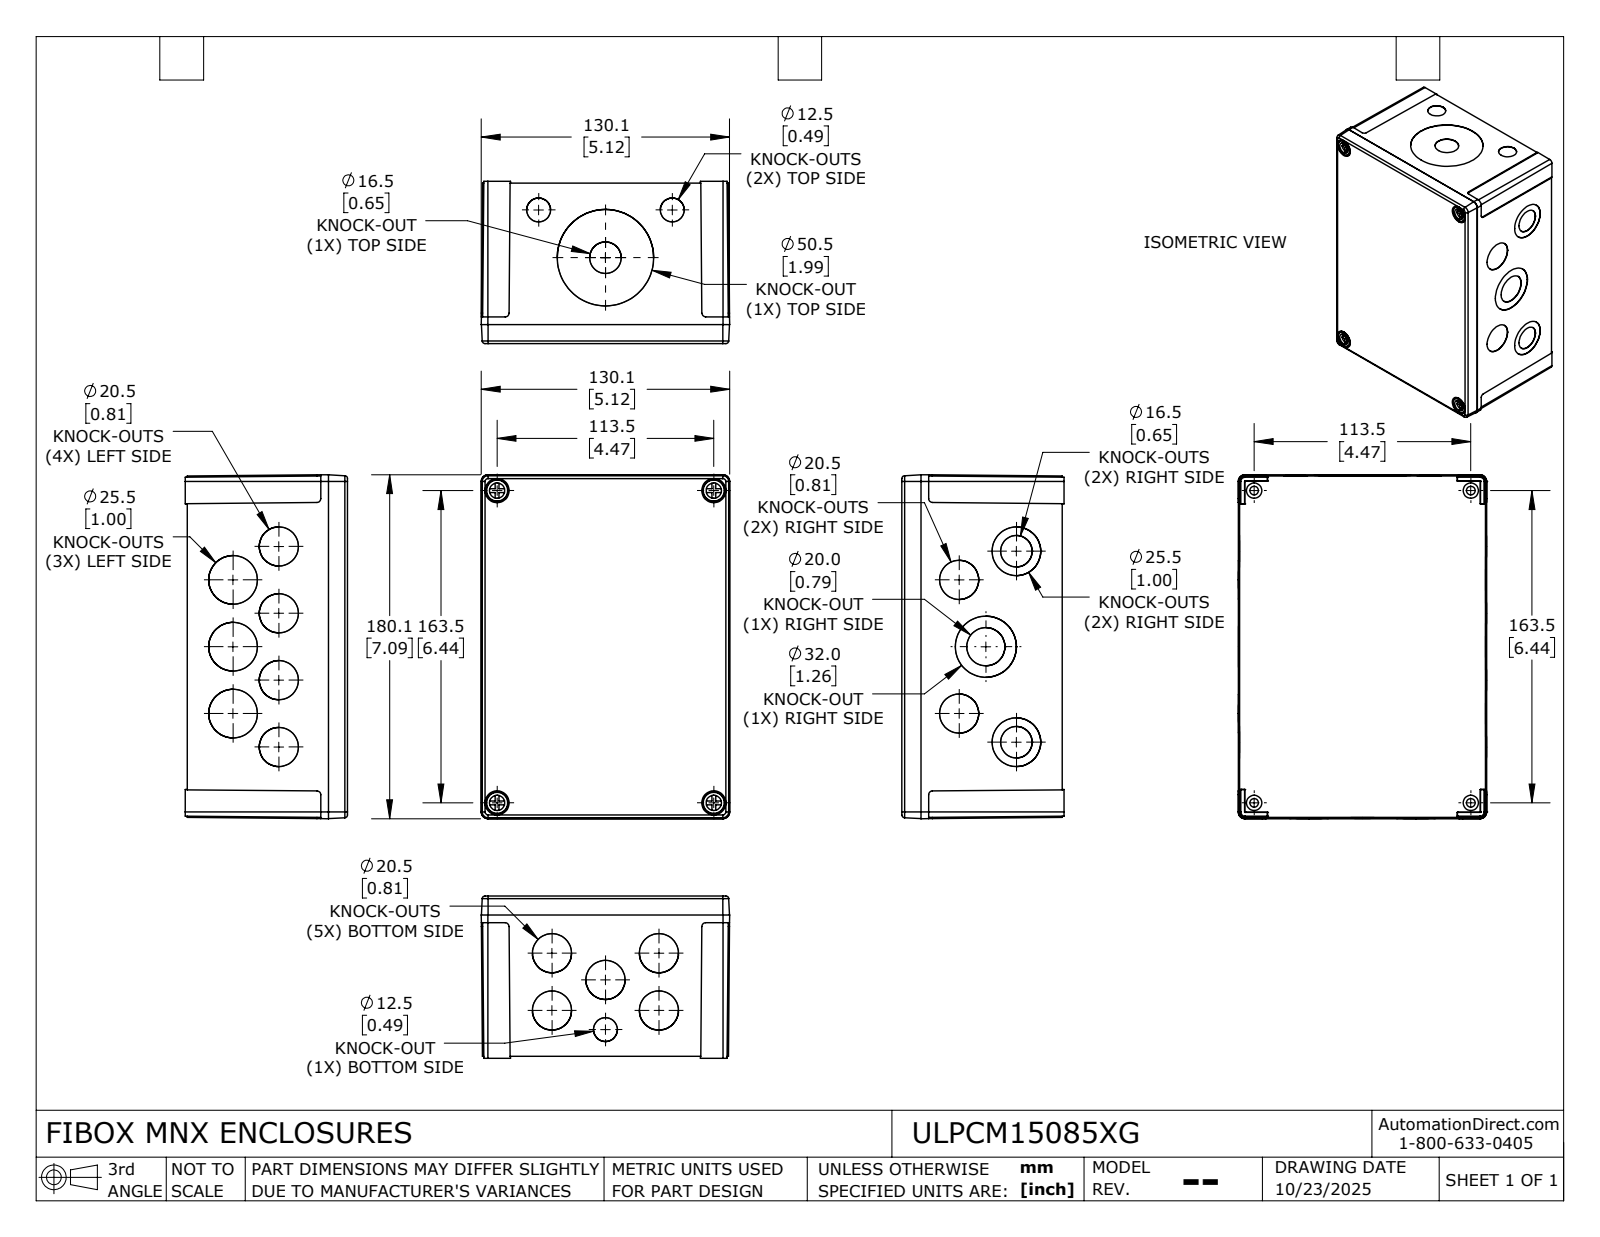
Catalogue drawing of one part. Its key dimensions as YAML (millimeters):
part_name: "ULPCM15085XG_Default"
step_written_by: "SolidWorks 2024 (CONFIG_CONTROL_DESIGN)"
units: millimeters
bodies: {solids: 6, faces: 564, planar: 290, cylindrical: 222, other: 52}
overall_size: [180.1, 130.1, 85]
volume: 366100
surface_area: 204300
round_holes:
  - {diameter: 20.5, count: 11}
  - {diameter: 3.2, count: 8}
  - {diameter: 4, count: 8}
  - {diameter: 25.5, count: 5}
  - {diameter: 4.5, count: 4}
  - {diameter: 8, count: 4}
  - {diameter: 11.6, count: 4}
  - {diameter: 12.5, count: 3}
  - {diameter: 16.5, count: 3}
  - {diameter: 20, count: 1}
  - {diameter: 32, count: 1}
  - {diameter: 50.5, count: 1}
round_bosses_or_shafts:
  - {diameter: 8, count: 8}
  - {diameter: 2.5, count: 8}
  - {diameter: 11, count: 4}
  - {diameter: 7.2, count: 4}
partial_cylinders:
  - {radius: 1, count: 16}
  - {radius: 1.4, count: 6}
  - {radius: 0.5, count: 4}
  - {radius: 1.5, count: 4}
  - {radius: 2, count: 4}
  - {radius: 5, count: 4}
  - {radius: 0.6, count: 2}
face_to_face_distances: [4.2, 84, 3.2, 80.8, 3, 81, 77.8, 4, 0.7, 0.5]
hole_center_spacings: [29.7, 35, 70, 33.9, 49.3, 50, 57.7, 57.9]
